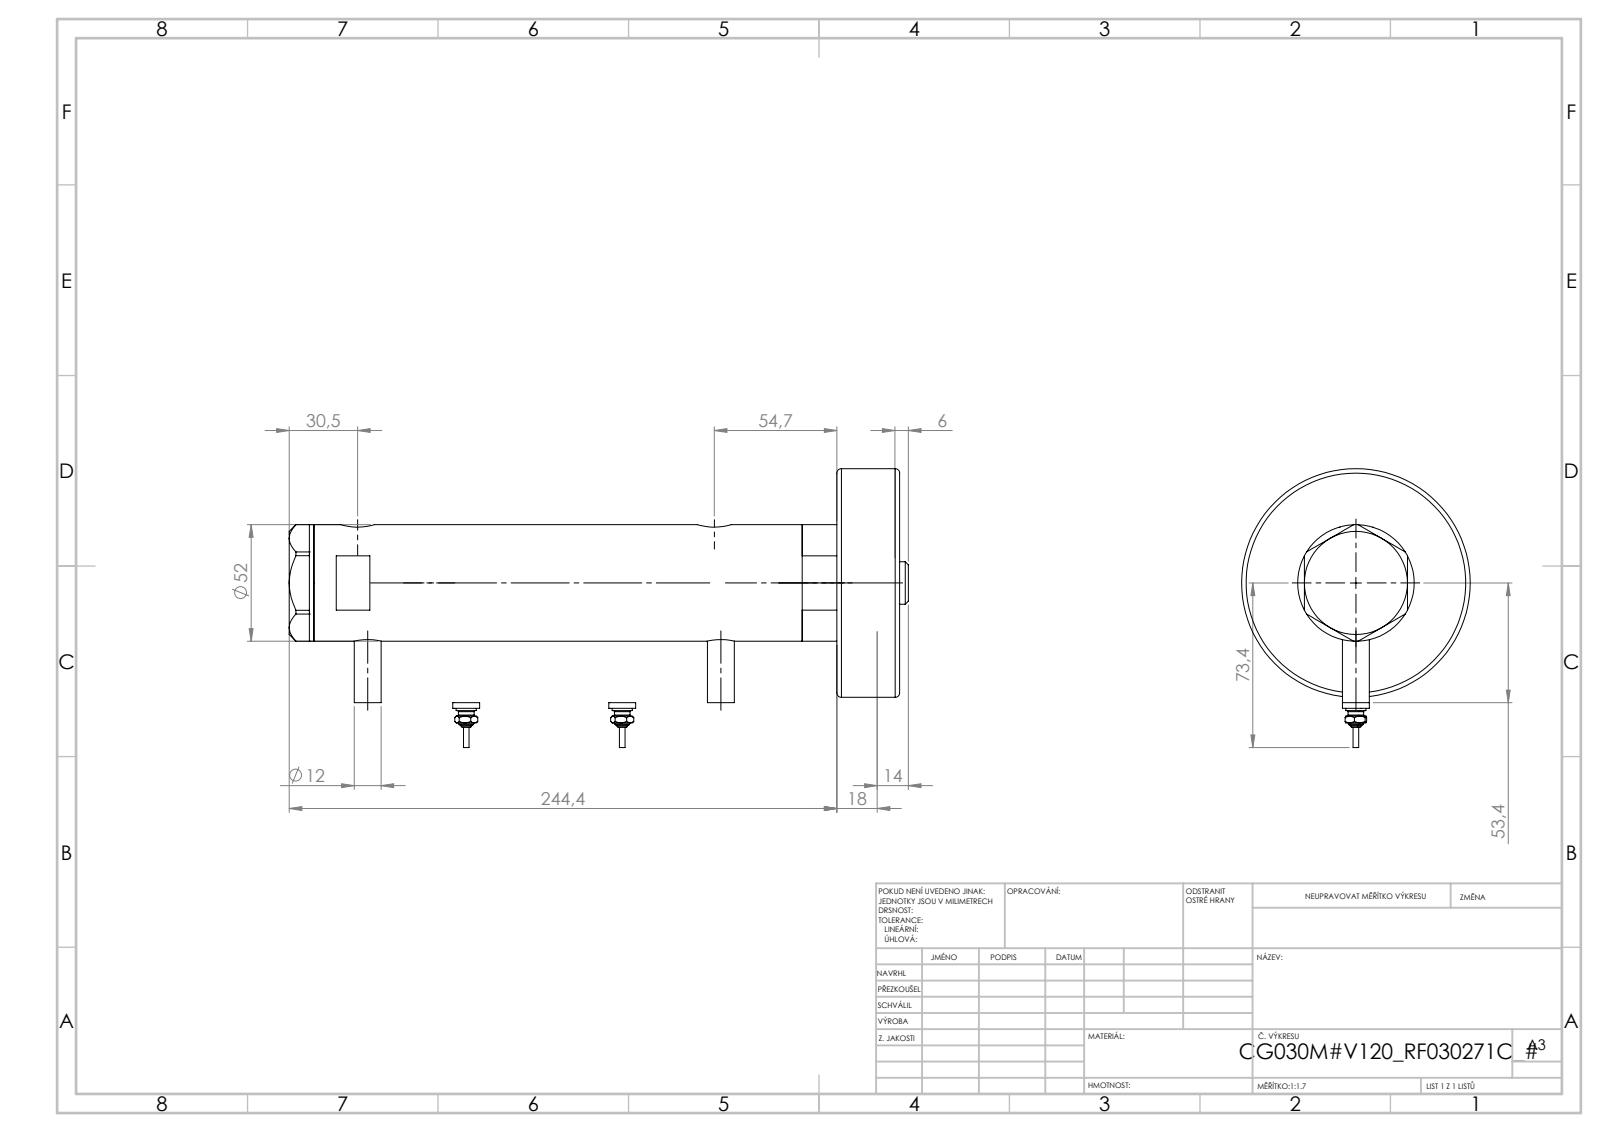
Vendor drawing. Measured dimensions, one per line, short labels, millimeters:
name: V270CG_SWITCH; V270CG_MIDDLE; V270CG_FRONT; V270CG_VC (+1 more)
written by: SolidWorks 2019 (CONFIG_CONTROL_DESIGN)
unit: mm
bodies: 6 solids, 246 faces (95 planar, 77 cylindrical, 74 other)
size: 269.02 × 84.3 × 52
volume: 478 097 mm³; area: 105 489 mm²
holes: 2× ⌀5, 2× ⌀9.73, 2× ⌀12.5, 2× ⌀15, 1× ⌀6.5, 1× ⌀20, 1× ⌀21.5, 1× ⌀30, 1× ⌀33, 1× ⌀44
bosses: 3× ⌀12, 2× ⌀9, 2× ⌀7, 2× ⌀4.34, 2× ⌀2.4, 1× ⌀52, 1× ⌀40, 1× ⌀38
face distances: 23.8, 11, 34.8, 46, 184.54, 173.54, 149.74, 220.94, 209.94, 186.14
hole spacings: 2.9, 4.5, 146.75, 149.65, 151.25, 154.15, 2.89, 2.91
